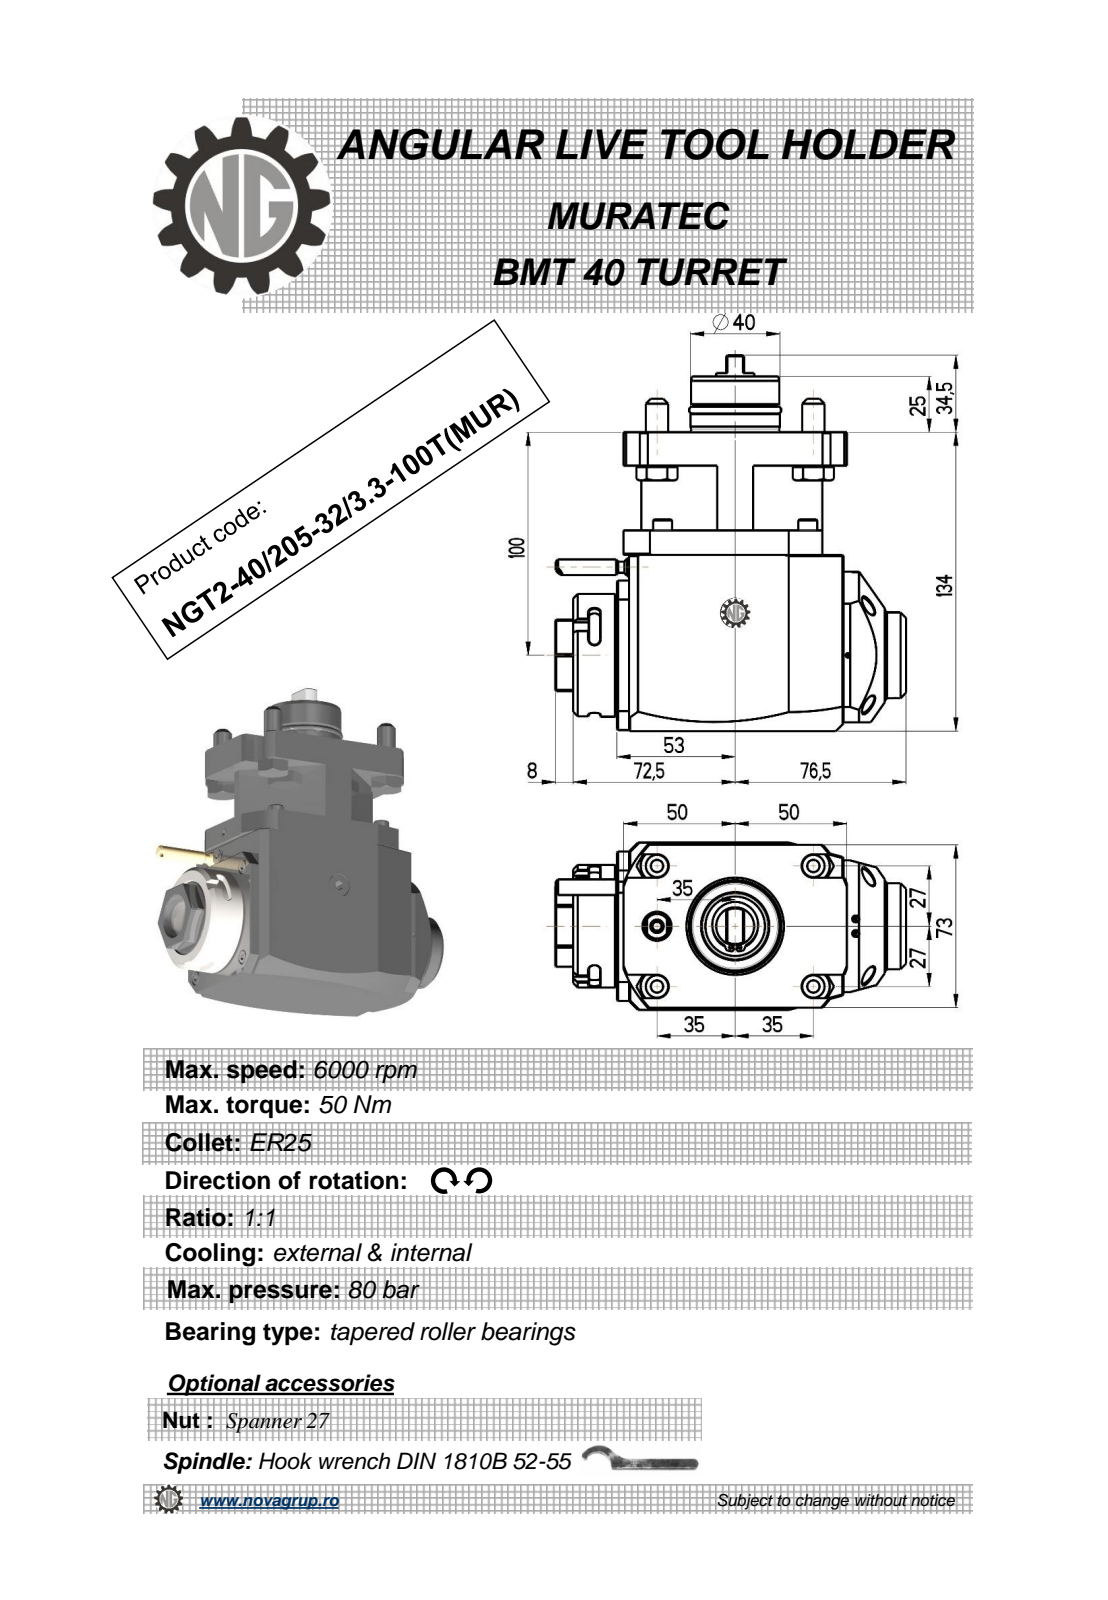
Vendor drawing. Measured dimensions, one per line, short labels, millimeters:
name: NGT2_40_205_32_3_3_100T_MUR
written by: PRO/ENGINEER BY PARAMETRIC TECHNOLOGY CORPORATION, 2010280 (CONFIG_CONTROL_DESIGN)
unit: mm
bodies: 2 solids, 369 faces (189 planar, 76 cylindrical, 104 other)
size: 168.5 × 157 × 75
volume: 1 012 000 mm³; area: 83 987 mm²
holes: 1× ⌀2.5, 1× ⌀3, 1× ⌀4.2, 1× ⌀9, 1× ⌀23
bosses: 4× ⌀14.6, 4× ⌀10, 1× ⌀55, 1× ⌀47, 1× ⌀40, 1× ⌀39.5, 1× ⌀39.4, 1× ⌀38.5
rounds: 6× R2.5, 4× R5.25, 2× R180, 1× R6, 1× R24.5, 1× R37.5, 1× R53.5
face distances: 75, 134, 1, 74, 63, 90, 44, 15, 29, 119
hole spacings: 43.2
